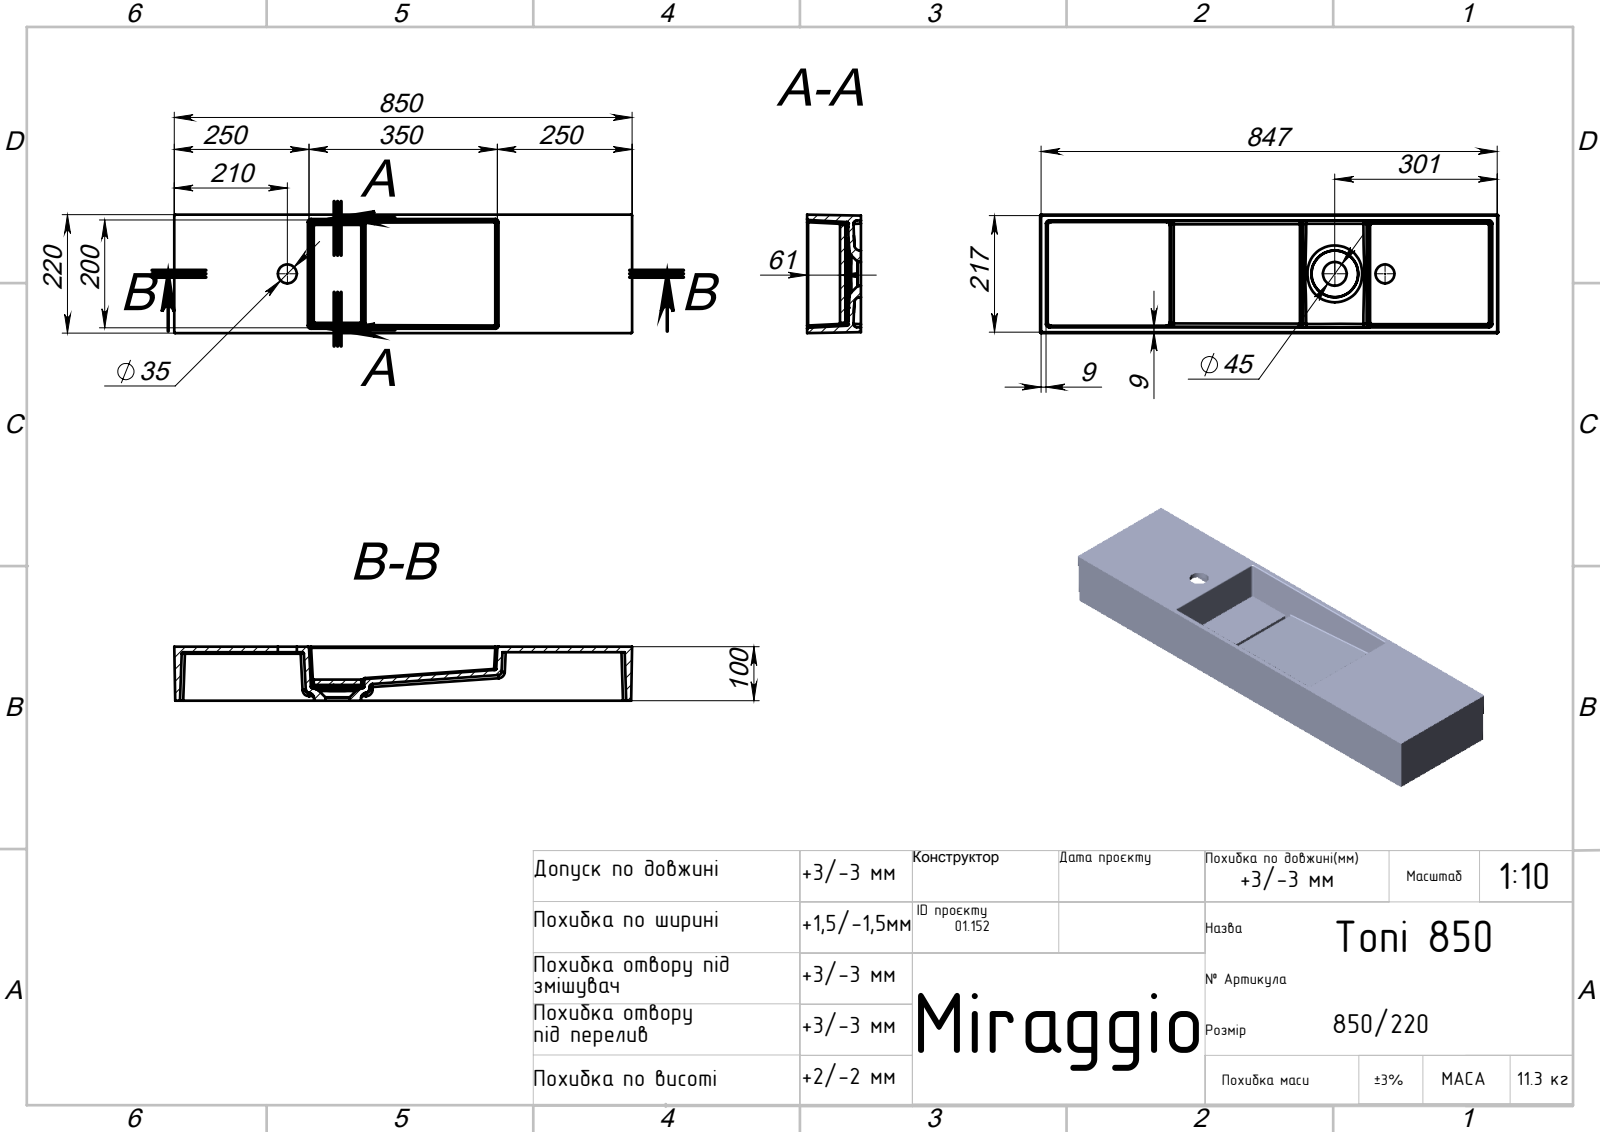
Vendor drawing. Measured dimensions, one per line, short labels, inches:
name: Toni 850
written by: SolidWorks 2020 (AUTOMOTIVE_DESIGN)
unit: in
bodies: 2 solids, 126 faces (32 planar, 44 cylindrical, 50 other)
size: 33.465 × 8.661 × 3.937
volume: 267.7 in³; area: 1 299 in²
holes: 2× ⌀0.394, 1× ⌀1.378, 1× ⌀1.772
rounds: 16× R0.079, 14× R0.236, 6× R0.157, 4× R0.118
face distances: 0.394, 2.402, 3.543, 3.937, 1.142, 2.795, 1.535, 2.008, 0.394, 9.586
hole spacings: 3.667, 28.602
